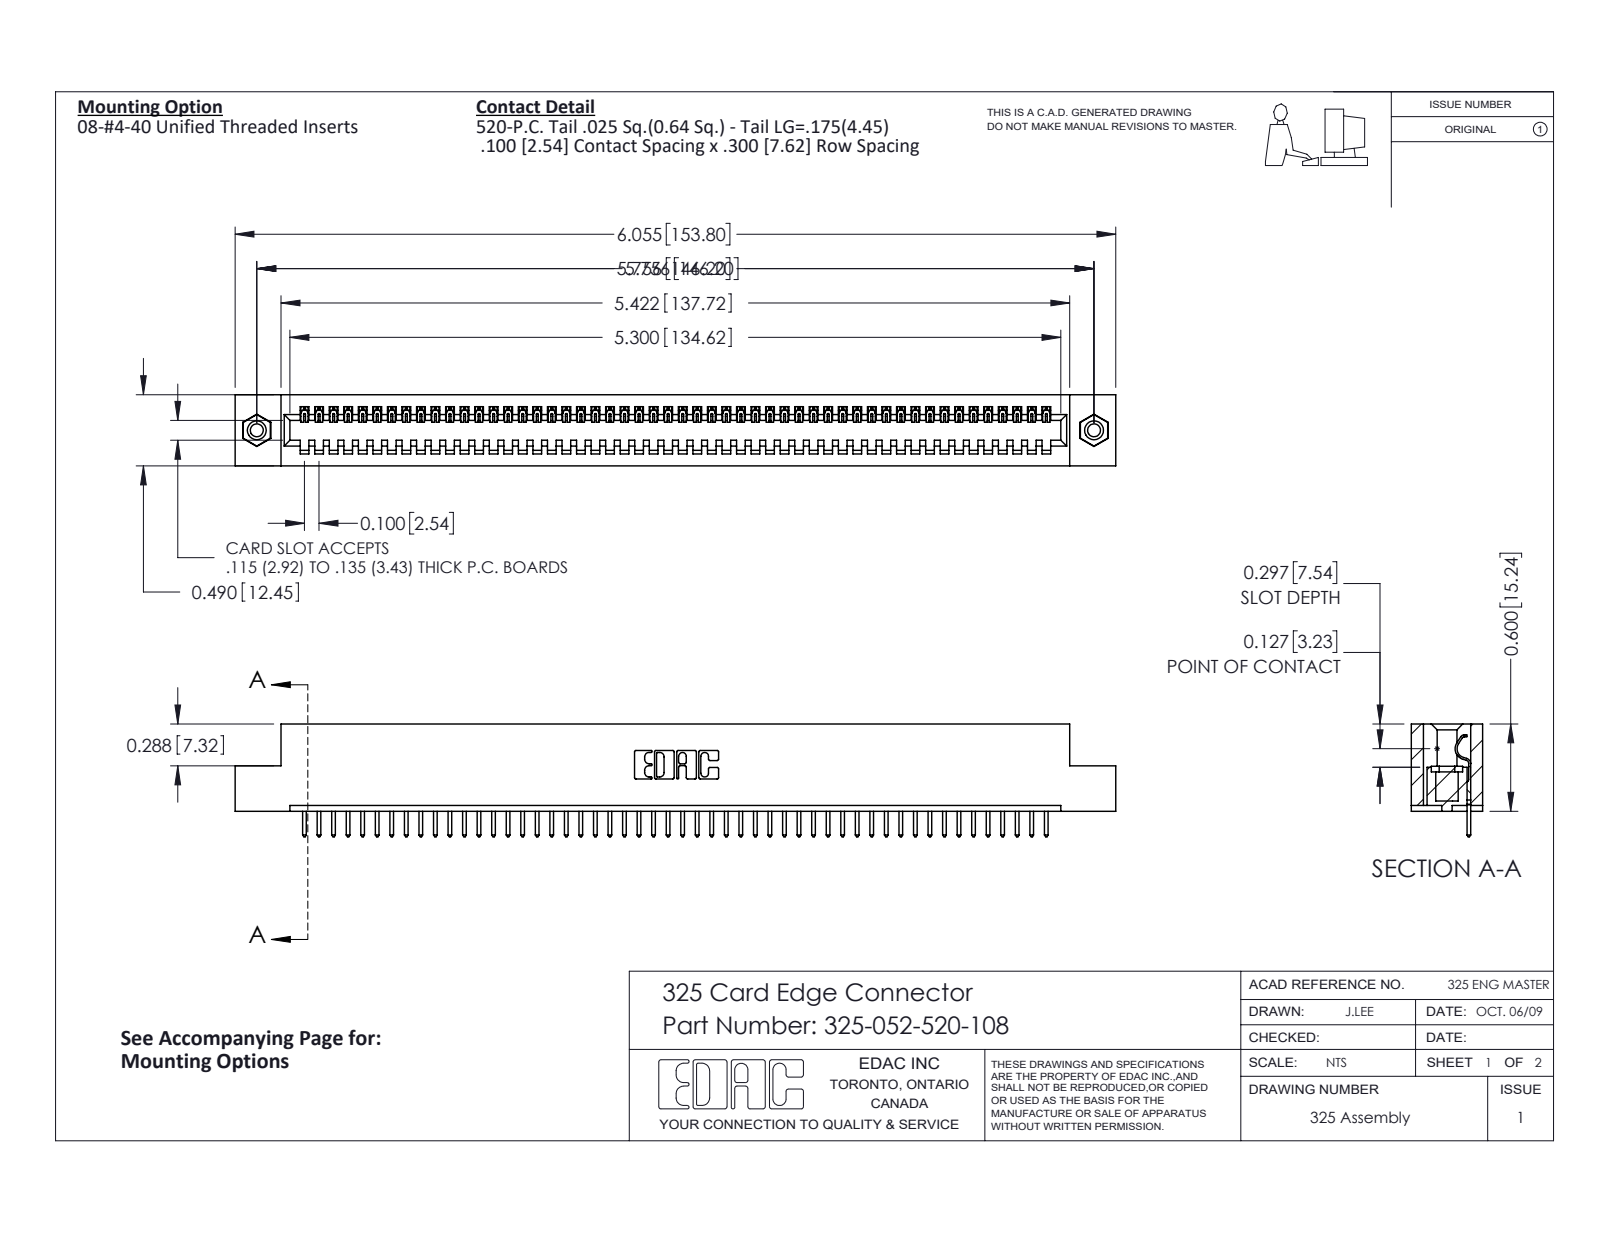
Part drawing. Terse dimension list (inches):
name: 325 Part_TI; 325-292-001_325-293-120; 345-250-001_345-250-003-102; 325-052-520-108
written by: SolidWorks 2016 (CONFIG_CONTROL_DESIGN)
unit: in
bodies: 55 solids, 3190 faces (2286 planar, 888 cylindrical, 16 other)
size: 6.055 × 0.775 × 0.49
volume: 1.188 in³; area: 32.4 in²
holes: 2× ⌀0.089, 2× ⌀0.125, 2× ⌀0.16
bosses: 2× ⌀0.155
rounds: 104× R0.006, 104× R0.01, 22× R0.01, 6× R0.007, 6× R0.031, 3× R0.026, 1× R0.014, 1× R0.022
face distances: 0.083, 0.407, 0.49, 0.3, 0.107, 0.383, 0.025, 0.325, 0.56, 0.263
hole spacings: 5.756
